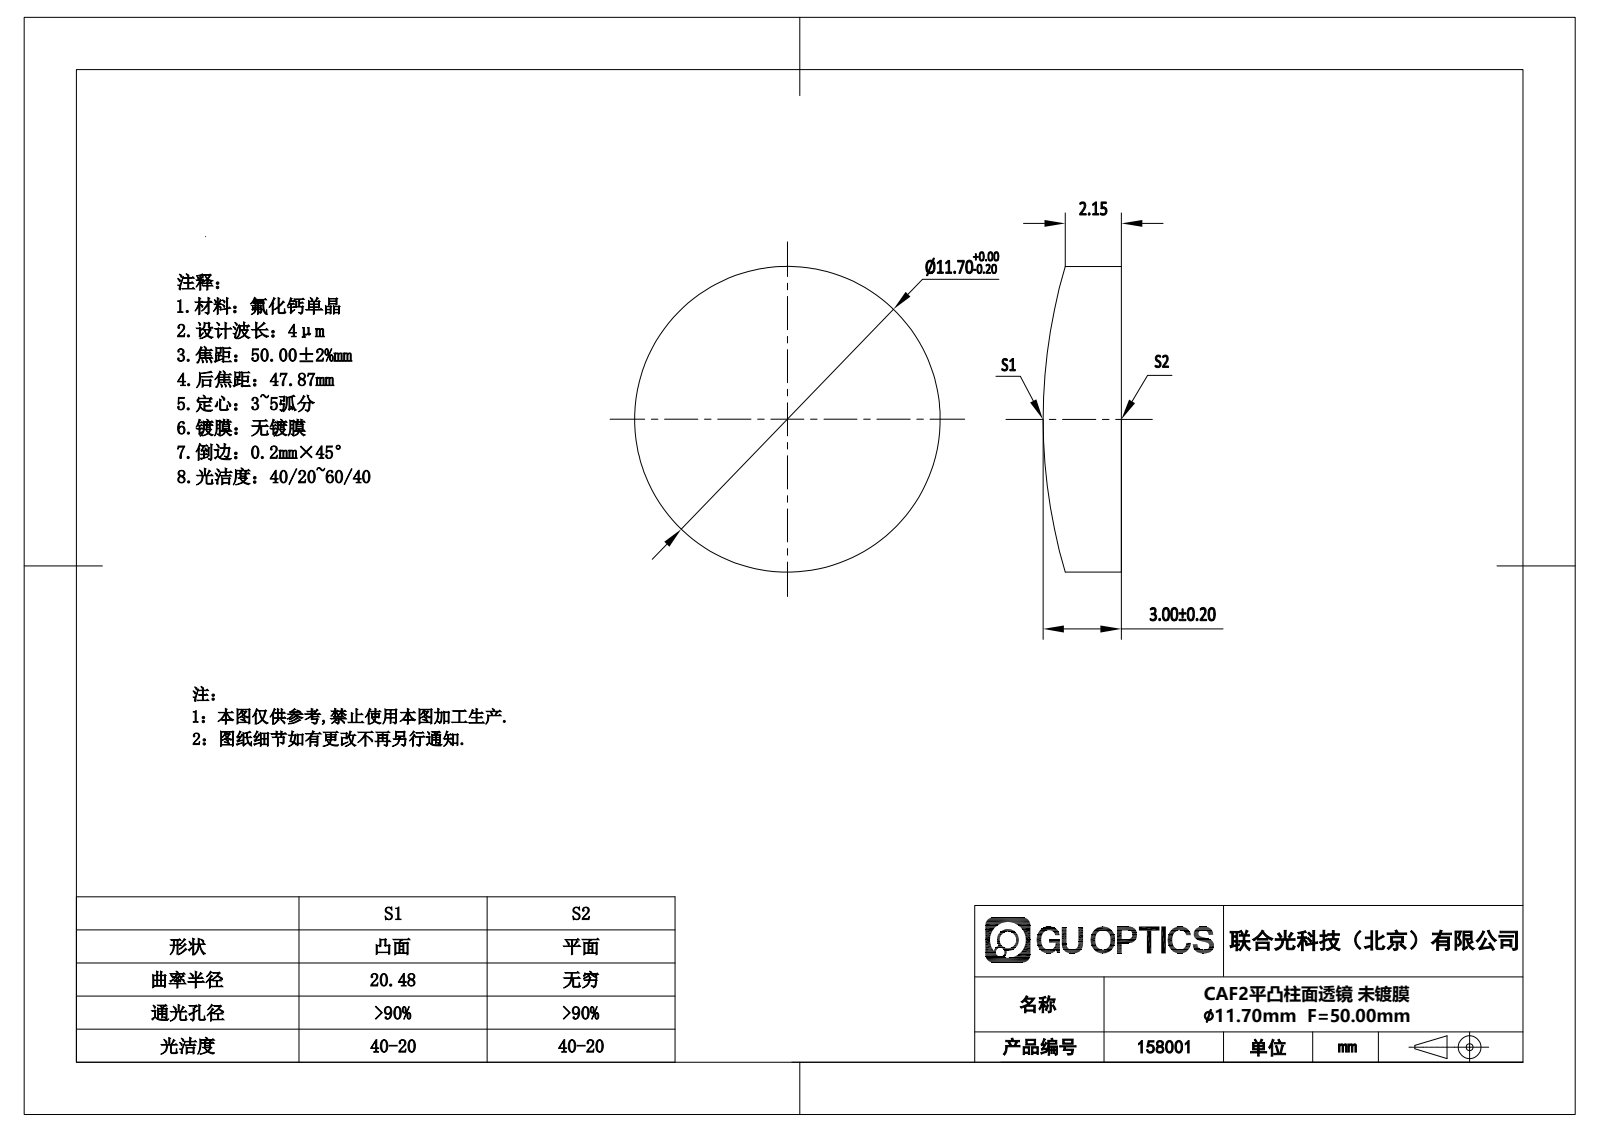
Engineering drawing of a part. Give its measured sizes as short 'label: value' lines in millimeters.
name: GL55-012-050
written by: SolidWorks 2022 (AUTOMOTIVE_DESIGN)
unit: mm
bodies: 1 solid, 9 faces (1 planar, 4 cylindrical, 4 other)
size: 11.7 × 11.7 × 3
volume: 299 mm³; area: 303 mm²
bosses: 1× ⌀11.7
rounds: 1× R20.48
